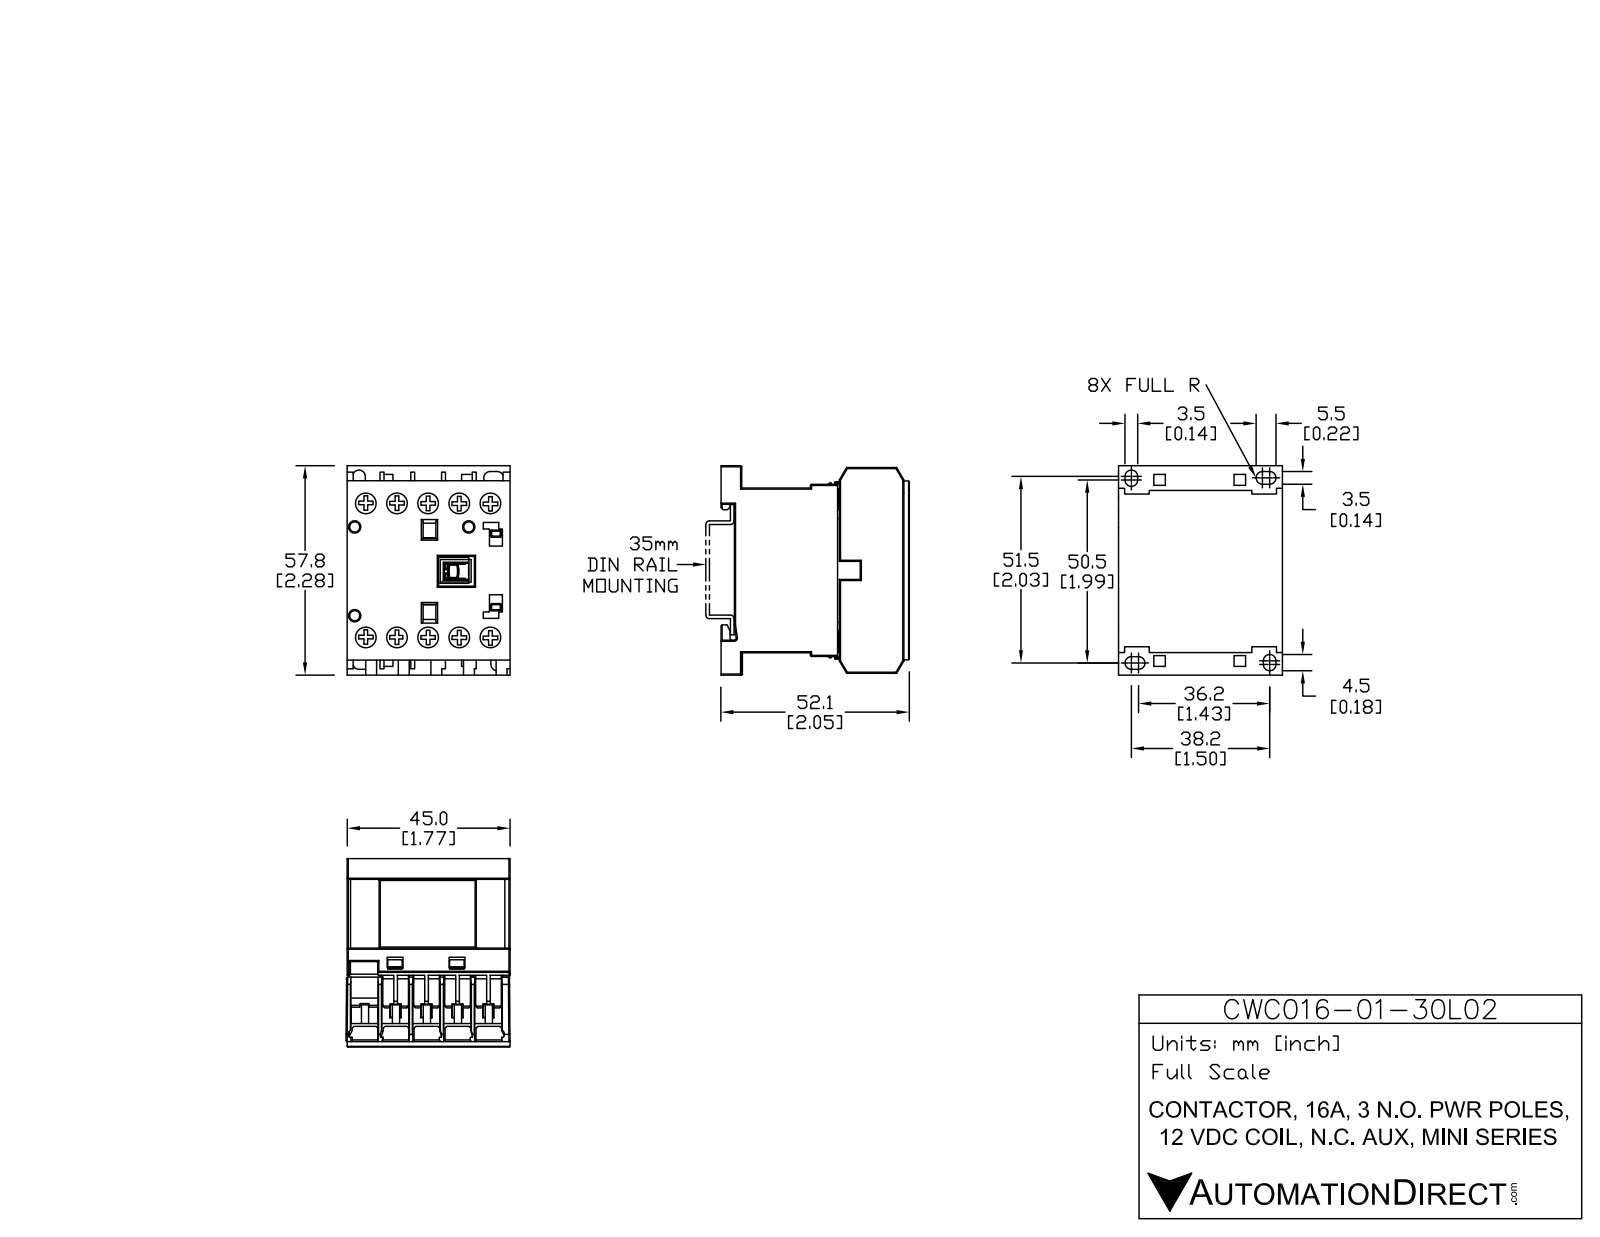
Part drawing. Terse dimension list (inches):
name: CWC16-01-30L02
written by: SolidWorks 2013 (AUTOMOTIVE_DESIGN)
unit: in
bodies: 15 solids, 535 faces (445 planar, 90 cylindrical, 0 other)
size: 2.285 × 2.052 × 1.801
volume: 5.927 in³; area: 47.18 in²
holes: 10× ⌀0.244, 3× ⌀0.11
bosses: 10× ⌀0.232
rounds: 20× R0.012, 6× R0.068, 2× R0.068, 1× R0.013, 1× R0.017, 1× R0.022
face distances: 0.325, 1.791, 0.049, 0.65, 0.374, 0.217, 0.699, 0.202, 0.419, 0.276
hole spacings: 0.337, 1.494, 0.673, 1.603, 1.455, 1.01, 1.771, 0.272
